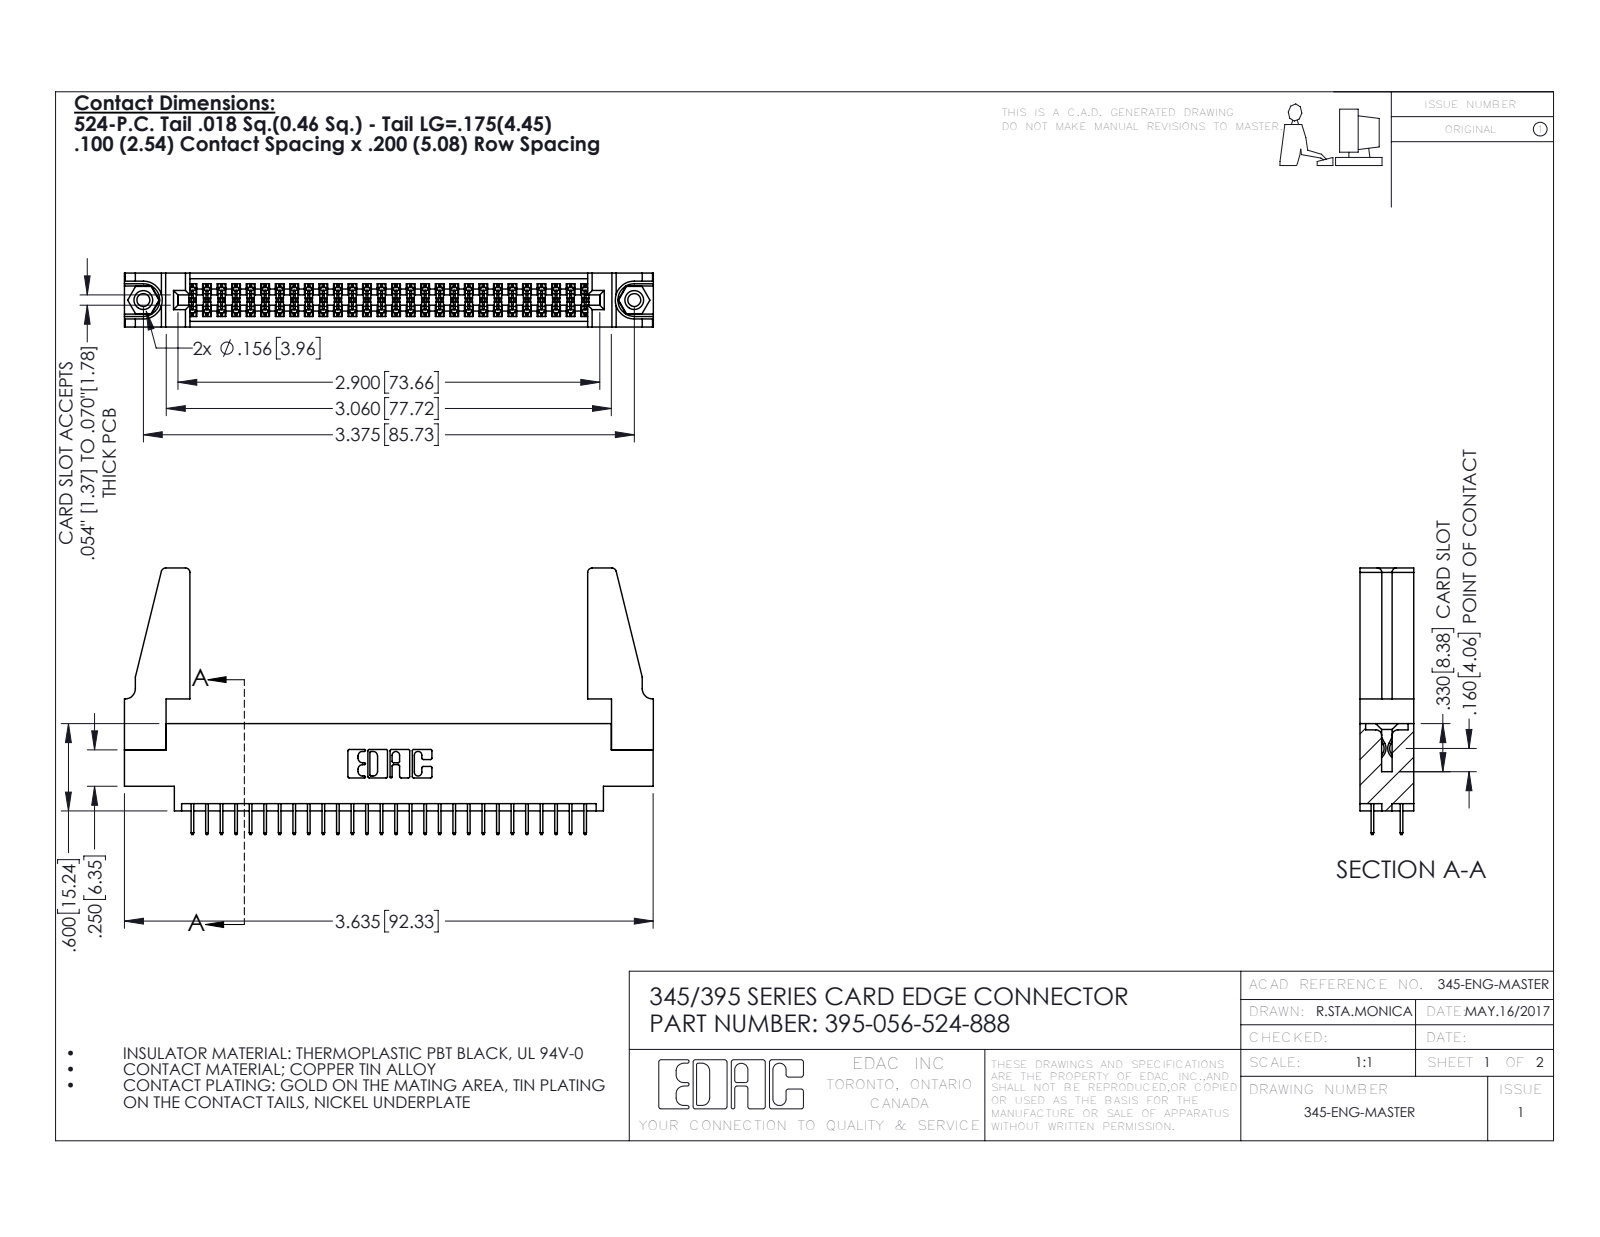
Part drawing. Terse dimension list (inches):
name: 395-056-524-888; 345-292-001_345-293-124; 345-250-001_345-250-001-102; 345 Part_0.170 Offset - 0.156 Dia-TH (+1 more)
written by: SolidWorks 2016 (CONFIG_CONTROL_DESIGN)
unit: in
bodies: 61 solids, 3278 faces (2340 planar, 922 cylindrical, 16 other)
size: 3.636 × 1.832 × 0.37
volume: 0.726 in³; area: 24.1 in²
holes: 2× ⌀0.089, 2× ⌀0.125, 2× ⌀0.156, 1× ⌀0.064
bosses: 2× ⌀0.155
rounds: 84× R0.006, 22× R0.01, 8× R0.03, 6× R0.007, 6× R0.031, 3× R0.026, 2× R0.014, 2× R0.019
face distances: 0.37, 0.072, 0.298, 0.2, 0.098, 0.272, 0.025, 0.225, 0.175, 0.072
hole spacings: 0.27, 3.14, 3.375
